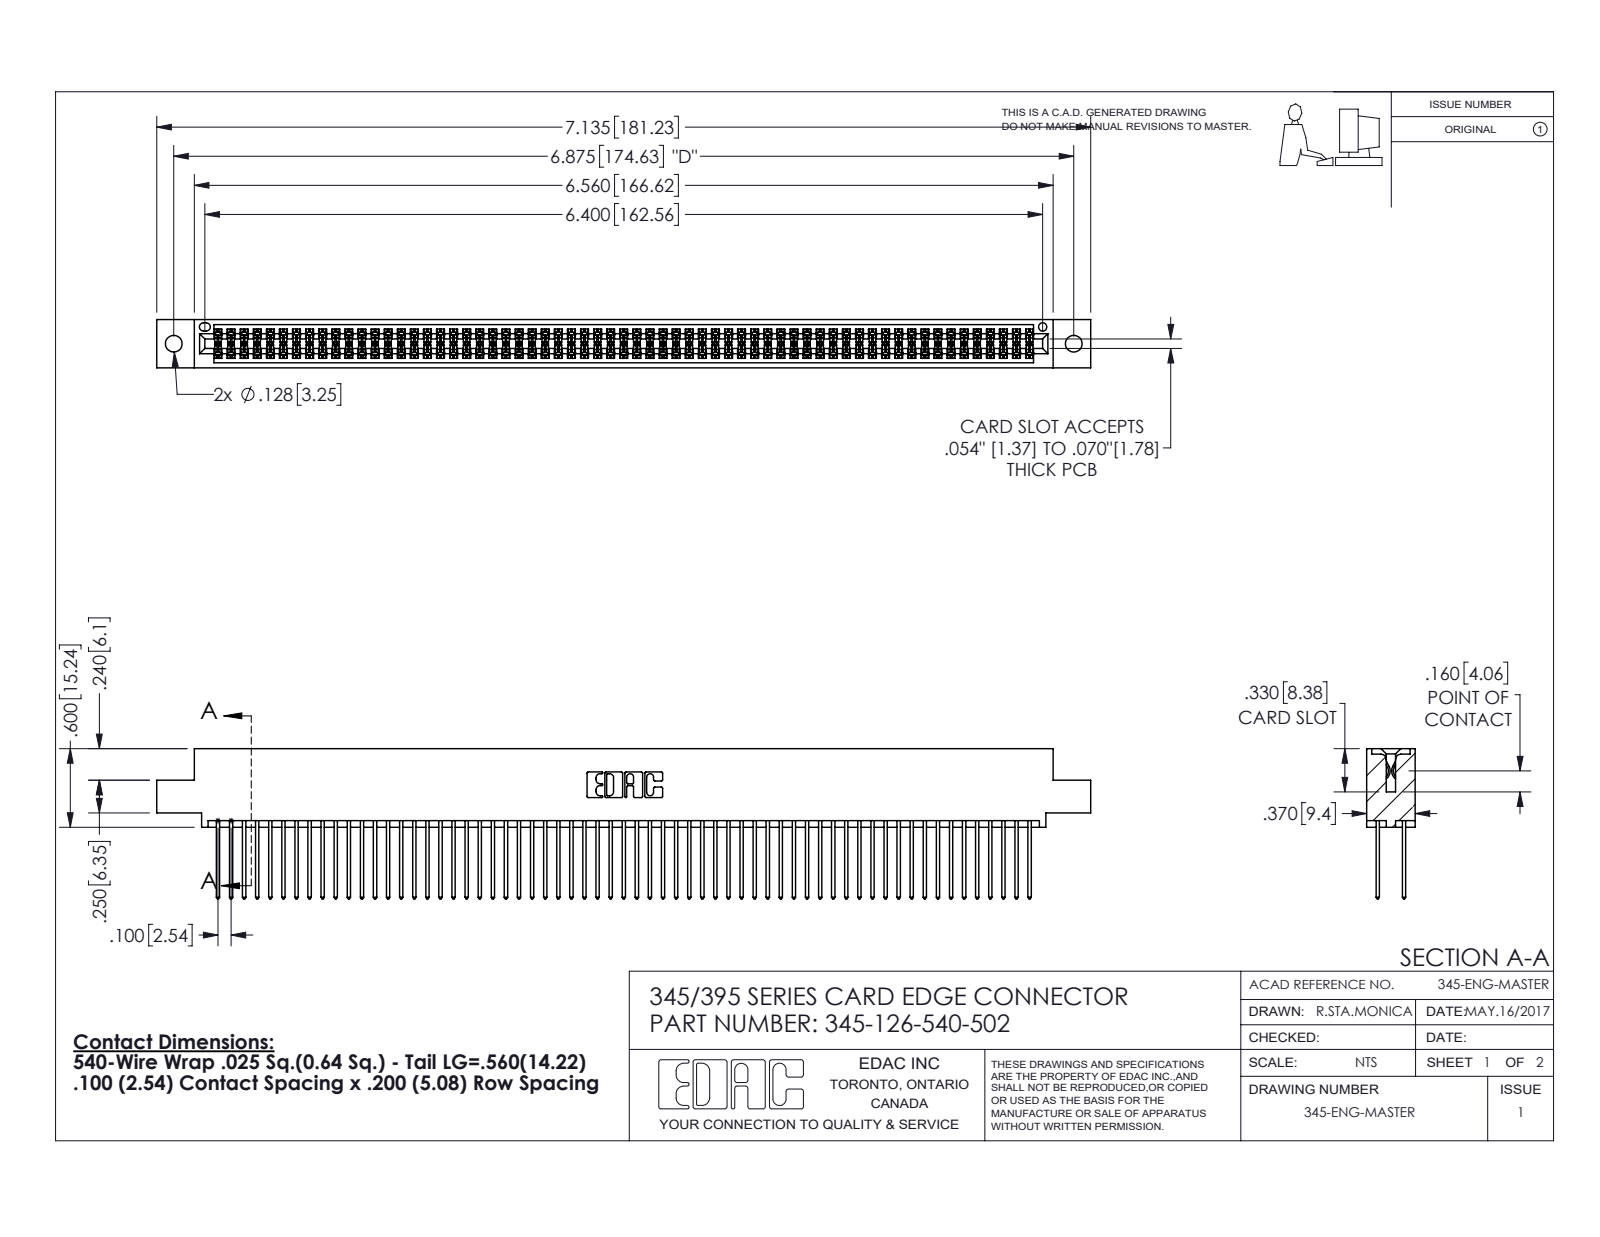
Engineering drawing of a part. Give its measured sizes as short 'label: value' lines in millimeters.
name: 345-126-540-502; 345-292-001_345-293-140; 345 Part_0.110 Offset - 0.128 Dia
written by: SolidWorks 2016 (CONFIG_CONTROL_DESIGN)
unit: mm
bodies: 127 solids, 6430 faces (4242 planar, 2188 cylindrical, 0 other)
size: 181.2 × 29.1 × 9.4
volume: 18 170 mm³; area: 29 300 mm²
holes: 2× ⌀3.3, 1× ⌀1.6
rounds: 189× R0.2, 126× R0.3, 22× R0.3, 6× R0.2, 6× R0.8, 3× R0.7, 2× R0.4, 2× R0.5
face distances: 7.6, 1.8, 5.1, 2.5, 6.9, 0.6, 5.7, 9.4, 4.4, 3.8
hole spacings: 6.9, 168.6, 174.6
